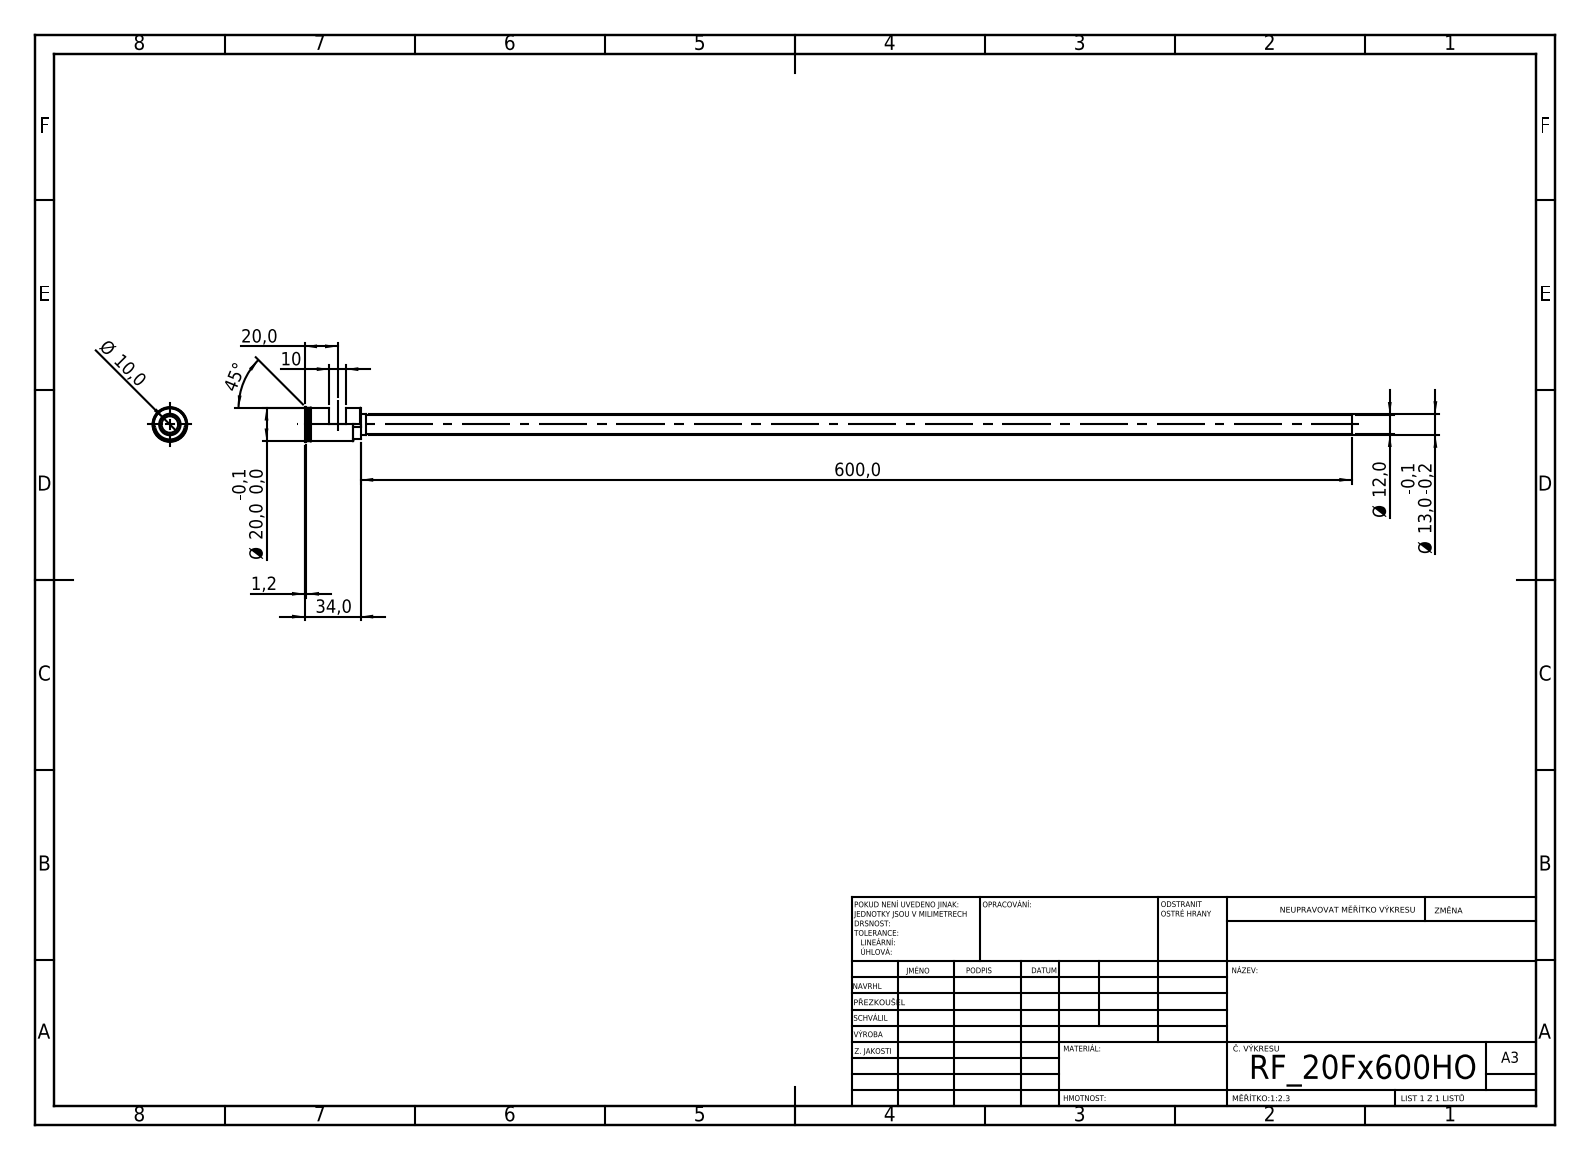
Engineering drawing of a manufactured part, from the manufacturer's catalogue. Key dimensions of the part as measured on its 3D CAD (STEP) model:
STEP written by: SolidWorks 2019 (CONFIG_CONTROL_DESIGN)
Units: millimetres
Bodies: 1 solid, 55 faces (24 planar, 19 cylindrical, 12 other)
Overall size (bounding box): 634 × 21 × 21
Volume: 28 333 mm³ · Surface area: 44 888 mm²
Round holes (diameter × count): ⌀10 ×1
Round bosses / shafts (diameter × count): ⌀21 ×1, ⌀20 ×1, ⌀19.8 ×1, ⌀13 ×1, ⌀12 ×1
Partial cylindrical surfaces — rounded edges, fillets, slot ends (radius × count): R3 ×2, R9.05 ×1
Main face-to-face distances: 13, 19, 32, 2, 34, 15, 9, 10, 23, 25
